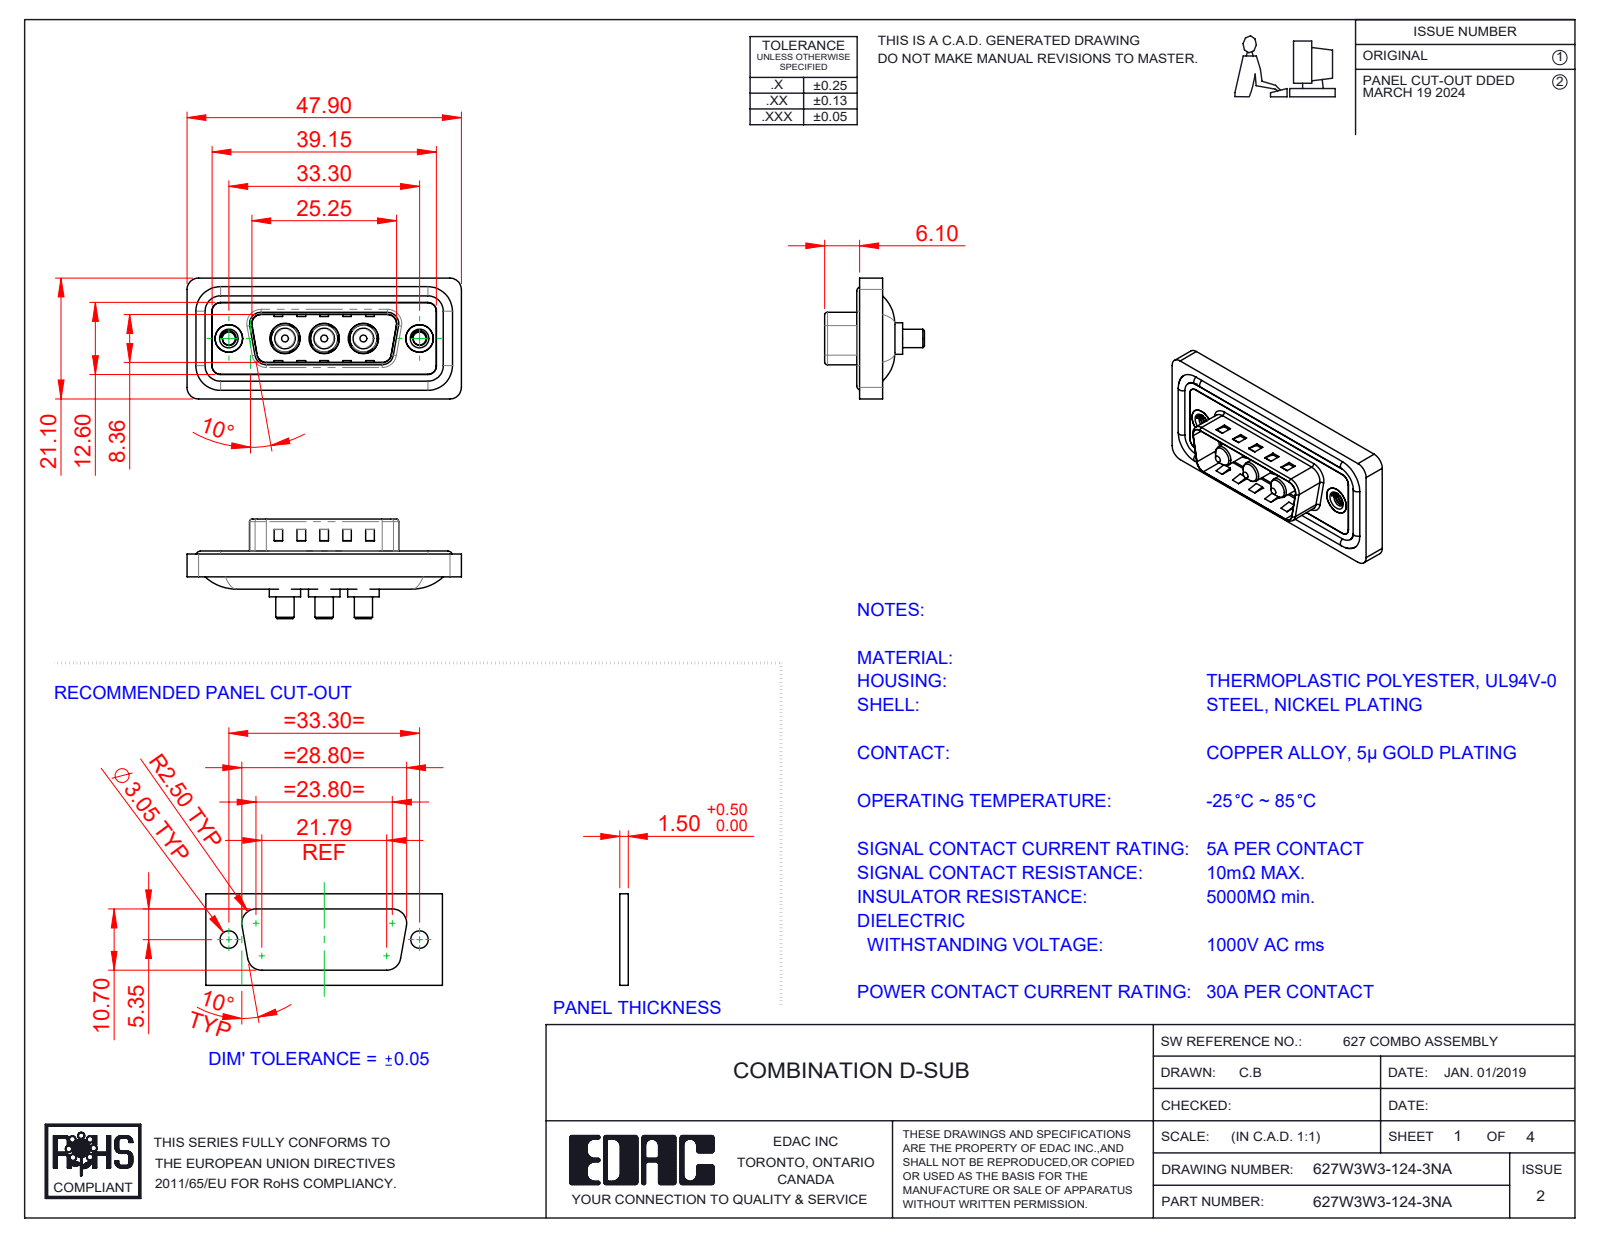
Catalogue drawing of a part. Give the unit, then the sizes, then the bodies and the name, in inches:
Units: inches
Overall size (bounding box): 1.886 × 0.831 × 0.685
Round holes (diameter × count): ⌀0.191 ×3, ⌀0.209 ×3, ⌀0.089 ×2, ⌀0.157 ×2, ⌀0.189 ×2, ⌀0.197 ×2
Round bosses / shafts (diameter × count): ⌀0.063 ×4, ⌀0.217 ×3, ⌀0.205 ×3, ⌀0.187 ×3, ⌀0.148 ×3, ⌀0.142 ×3, ⌀0.126 ×3, ⌀0.193 ×2
Partial cylindrical surfaces — rounded edges, fillets, slot ends (radius × count): R0.059 ×26, R0.079 ×20, R0.02 ×8, R0.063 ×8, R0.01 ×4, R0.024 ×4, R0.026 ×4, R0.035 ×4
Main face-to-face distances: 0.016, 0.043, 0.059, 0.02, 0.063, 0.122, 0.114, 0.157, 0.032, 0.377
Hole centre spacings: 0.27, 0.386, 0.656, 0.925, 0.539, 1.311
Volume: 0.342 in³ · Surface area: 13.59 in²
Bodies: 13 solids, 562 faces (207 planar, 243 cylindrical, 112 other)
Part name (STEP PRODUCT): 627Combo Housing_3W3; Power Pin_30A S; 627W3W3-124-3NA; 627Combo Threaded Rivet_A (+3 more)
STEP written by: SolidWorks 2023 (CONFIG_CONTROL_DESIGN)
